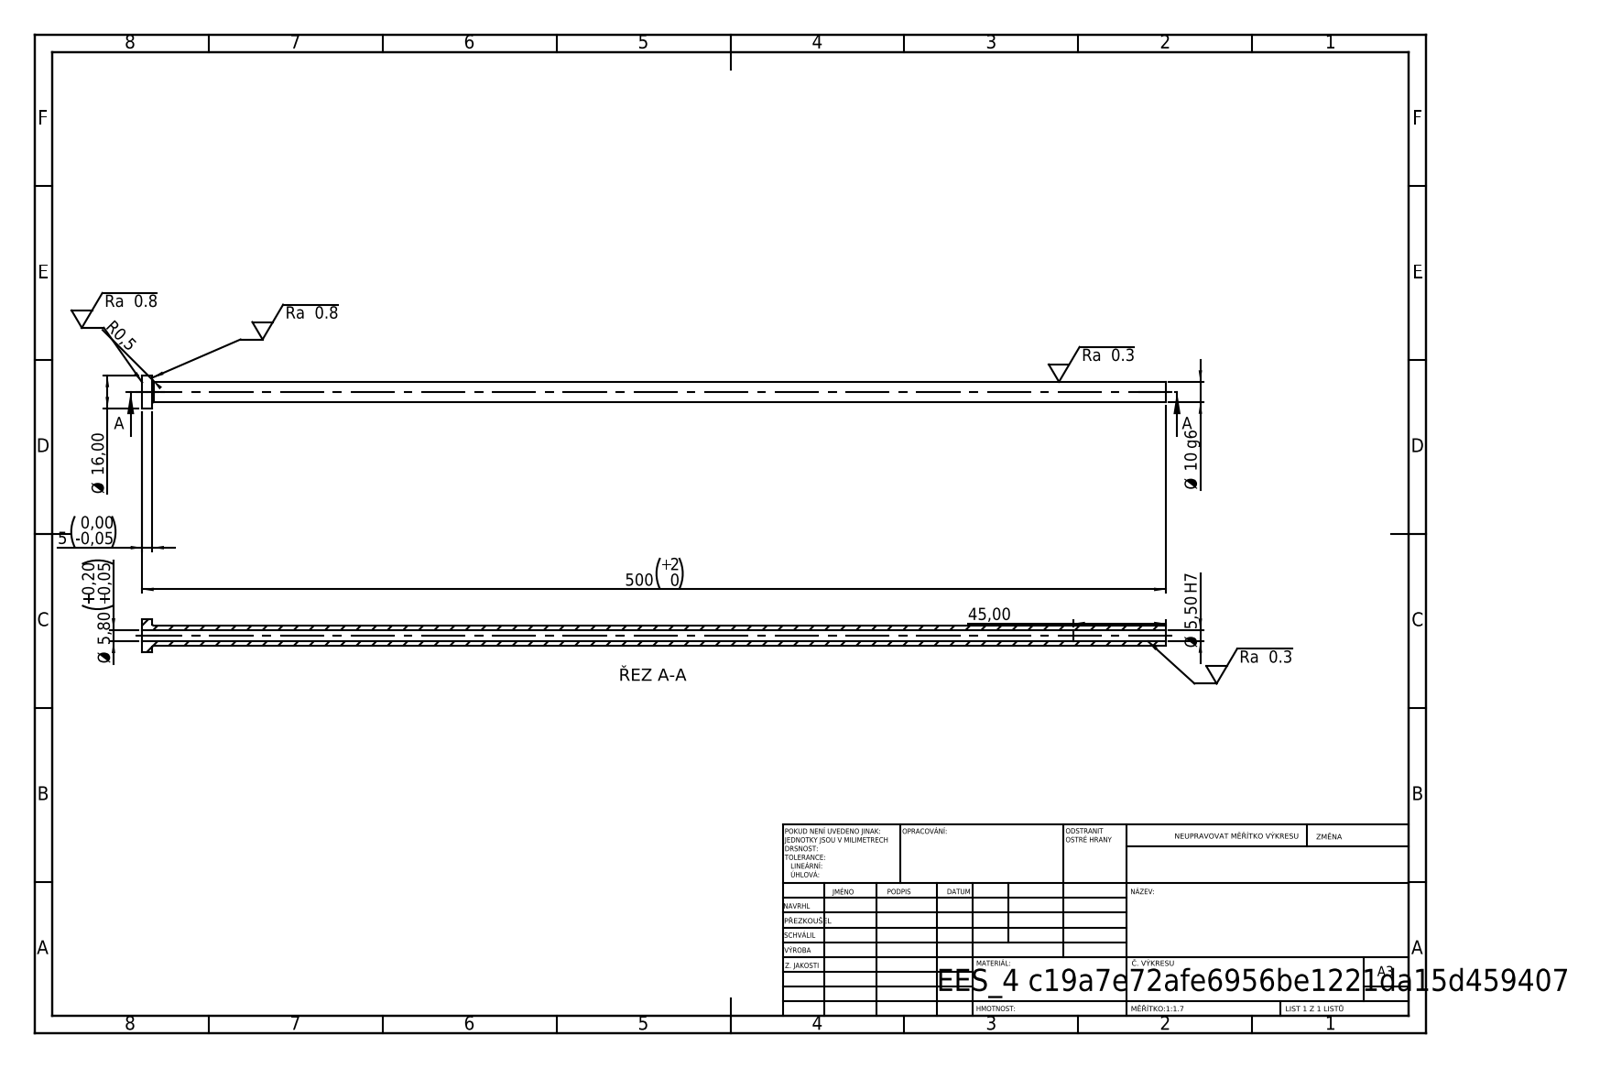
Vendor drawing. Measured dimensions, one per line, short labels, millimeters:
written by: SolidWorks 2019 (CONFIG_CONTROL_DESIGN)
unit: mm
bodies: 1 solid, 14 faces (4 planar, 8 cylindrical, 2 other)
size: 500 × 16 × 16
volume: 26 794 mm³; area: 25 218 mm²
holes: 1× ⌀5.5, 1× ⌀5.8
bosses: 1× ⌀16, 1× ⌀10
face distances: 5, 500, 495, 455, 450, 45
